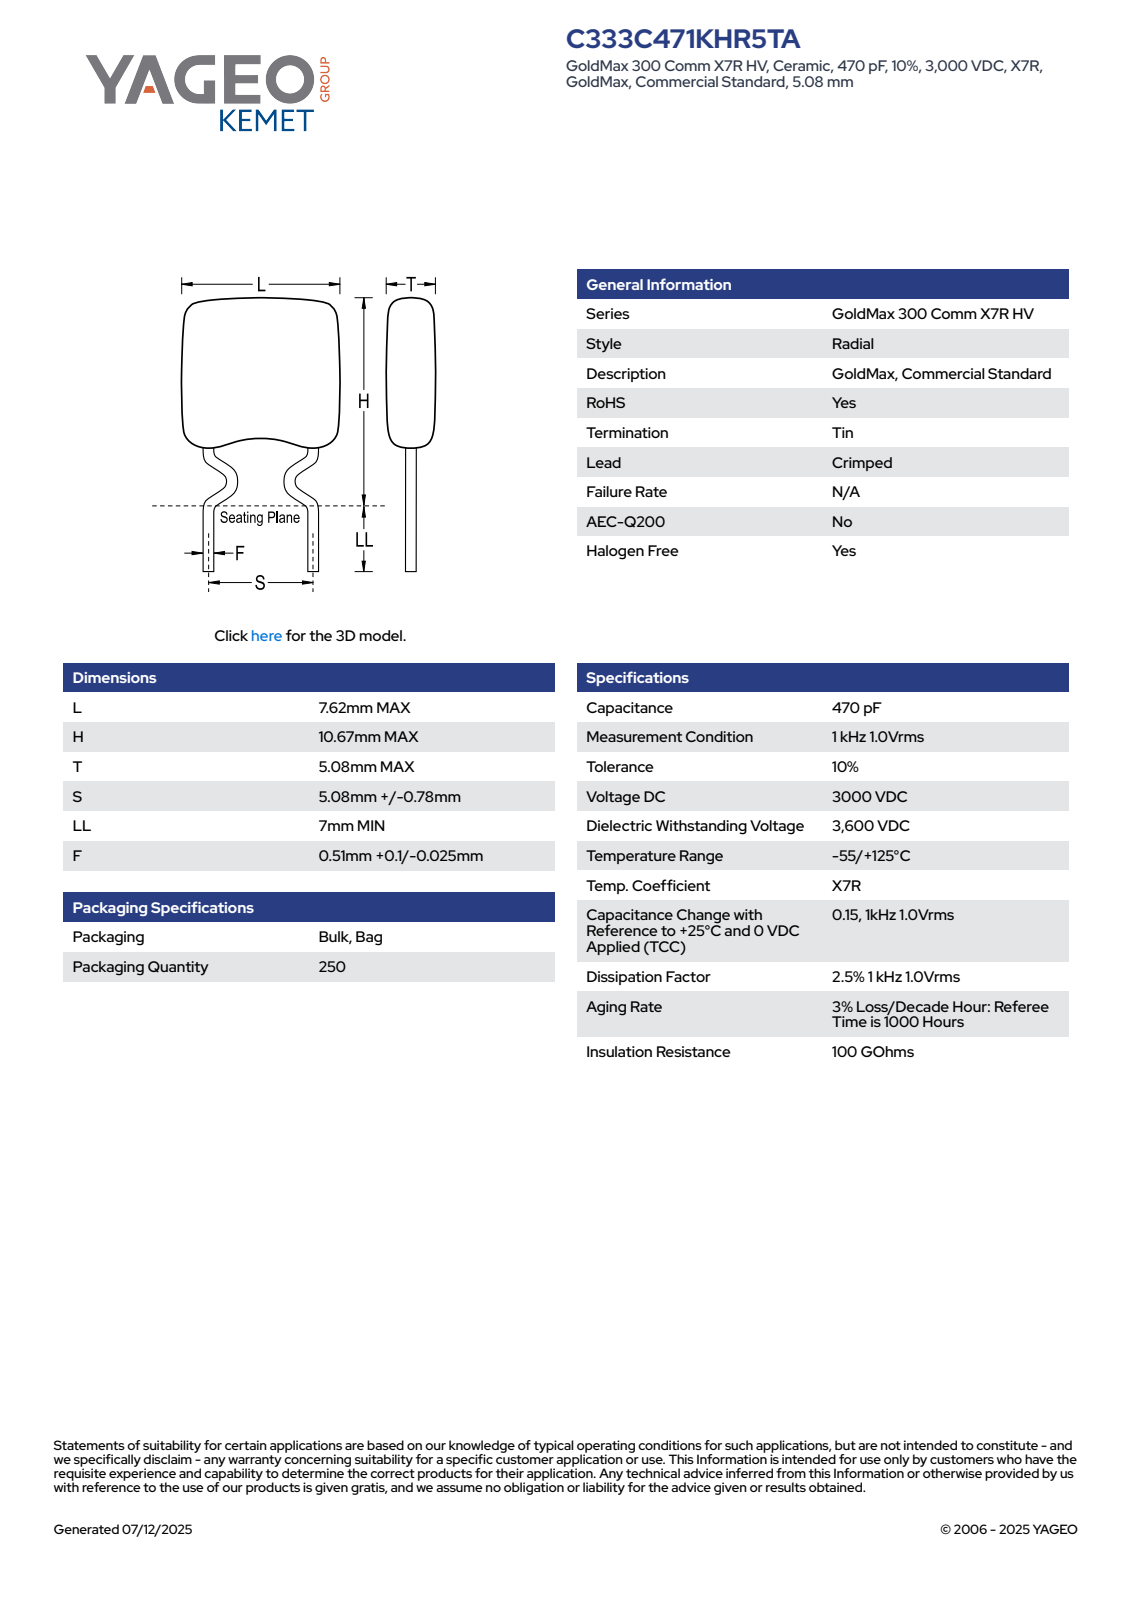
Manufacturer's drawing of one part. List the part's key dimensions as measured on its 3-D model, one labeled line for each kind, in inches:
Part name (STEP PRODUCT): CCRC333_L7.62H10.67T5.08S5.08LL7F0.61
STEP written by: SolidWorks 2014 (AUTOMOTIVE_DESIGN)
Units: inches
Bodies: 4 solids, 112 faces (66 planar, 18 cylindrical, 28 other)
Overall size (bounding box): 0.696 × 0.3 × 0.2
Volume: 0.016 in³ · Surface area: 0.428 in²
Round bosses / shafts (diameter × count): ⌀0.024 ×2
Partial cylindrical surfaces — rounded edges, fillets, slot ends (radius × count): R0.039 ×12
Main face-to-face distances: 0.2, 0.3, 0.278, 0.041, 0.16, 0.118, 0.119, 0.159, 0.033, 0.015
